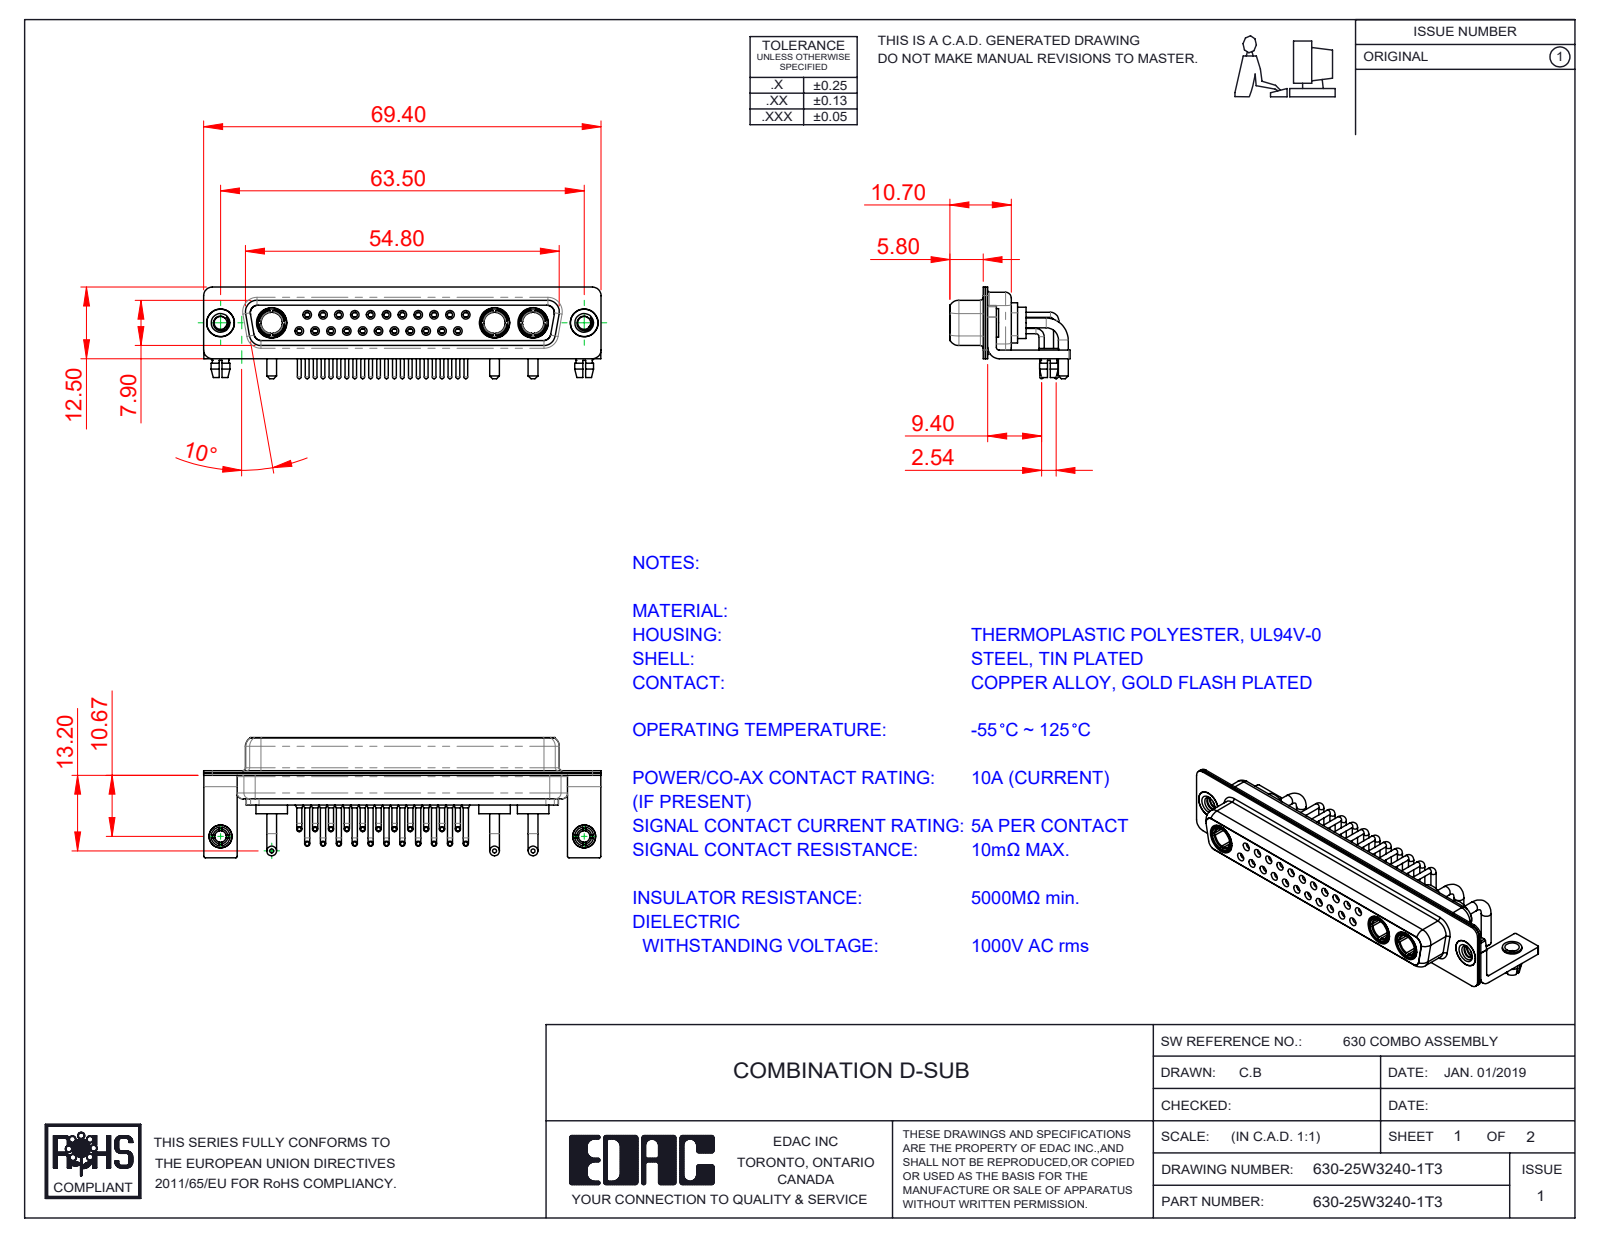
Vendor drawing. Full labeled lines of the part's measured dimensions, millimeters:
Part name (STEP PRODUCT): 630Combo Shell Front_37 Contacts; Power Socket_10A RA; 630Combo Contact Row 1; 630Combo Board Lock (+6 more)
STEP written by: SolidWorks 2020 (CONFIG_CONTROL_DESIGN)
Units: millimetres
Bodies: 37 solids, 1811 faces (552 planar, 768 cylindrical, 491 other)
Overall size (bounding box): 69.4 × 21 × 16
Volume: 5 806 mm³ · Surface area: 13 360 mm²
Round holes (diameter × count): ⌀2 ×24, ⌀0.9 ×22, ⌀1.1 ×22, ⌀1.5 ×22, ⌀1.6 ×11, ⌀1.7 ×11, ⌀4.85 ×5, ⌀3.7 ×3, ⌀5.3 ×3, ⌀2.26 ×2, ⌀2.5 ×2, ⌀3.2 ×2
Round bosses / shafts (diameter × count): ⌀0.9 ×23, ⌀0.65 ×22, ⌀1.6 ×12, ⌀1.7 ×6, ⌀5.5 ×3, ⌀5.2 ×3, ⌀4.96 ×3, ⌀4.75 ×3
Partial cylindrical surfaces — rounded edges, fillets, slot ends (radius × count): R0.25 ×16, R1.5 ×16, R2 ×13, R1.35 ×8, R1.6 ×8, R0.5 ×5, R0.6 ×4, R0.65 ×4
Main face-to-face distances: 0.4, 0.45, 1.4, 8.45, 1.8, 8.9, 6.2, 7.05, 0.8, 7.5
Hole centre spacings: 3.16, 2.77, 5.54, 5.03, 8.31, 7.48, 11.08, 5.04
